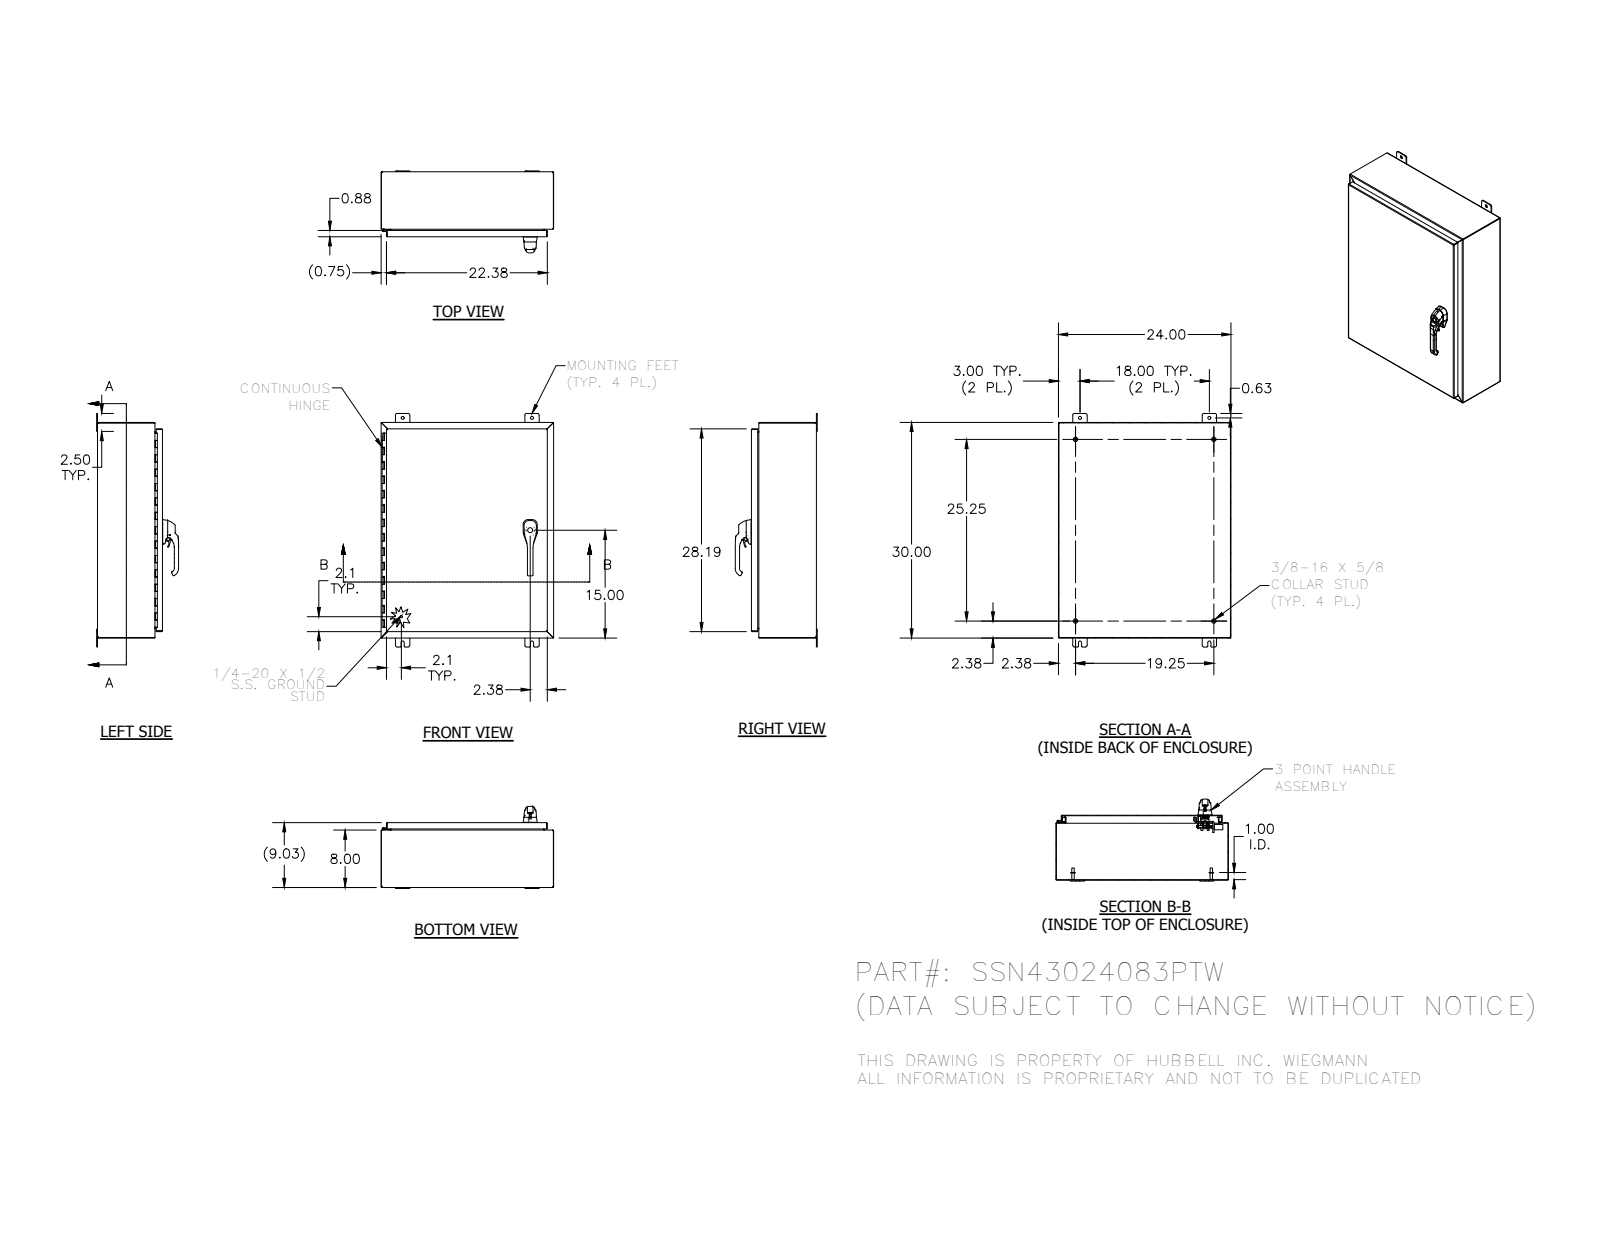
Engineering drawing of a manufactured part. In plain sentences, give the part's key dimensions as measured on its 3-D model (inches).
The part is named "30254; PLASTIC-ROLLER-CAM_AF1; 328139; DIN3771_16X2_5 (+8 more)". Its 3-D file was written by "SolidWorks 2014 (AUTOMOTIVE_DESIGN)". It is 56 solids with 3128 faces: 1047 planar, 1296 cylindrical and 785 other. Overall it measures 32.5 by 24 by 11.408 inches. Its volume is 217.2 cubic inches and its surface area 5 615 square inches. Round holes: 8 of diameter 0.262, 4 of diameter 0.187, 4 of diameter 0.438, 3 of diameter 0.213, 3 of diameter 0.281, 2 of diameter 0.241, 2 of diameter 0.25, 2 of diameter 0.252, 2 of diameter 0.315, 2 of diameter 0.4, 2 of diameter 0.402, 2 of diameter 0.413. Round bosses or shafts: 4 of diameter 0.625, 4 of diameter 0.33, 3 of diameter 0.236, 2 of diameter 1, 2 of diameter 0.563, 2 of diameter 0.533, 2 of diameter 0.531, 2 of diameter 0.5. Partial cylindrical surfaces (rounded edges, fillets, slot ends): 172 of radius 0.02, 113 of radius 0.012, 26 of radius 0.125, 24 of radius 0.031, 21 of radius 0.019, 20 of radius 0.105, 20 of radius 0.25, 16 of radius 0.025. The main face-to-face distances are 0.074, 8.959, 8.885, 9.033, 23.926, 29.926, 7.926, 1.033, 23.852, 24. The hole center spacings are 0.38, 0.492, 0.76, 0.886, 20.428, 0.234, 0.258, 0.38.
